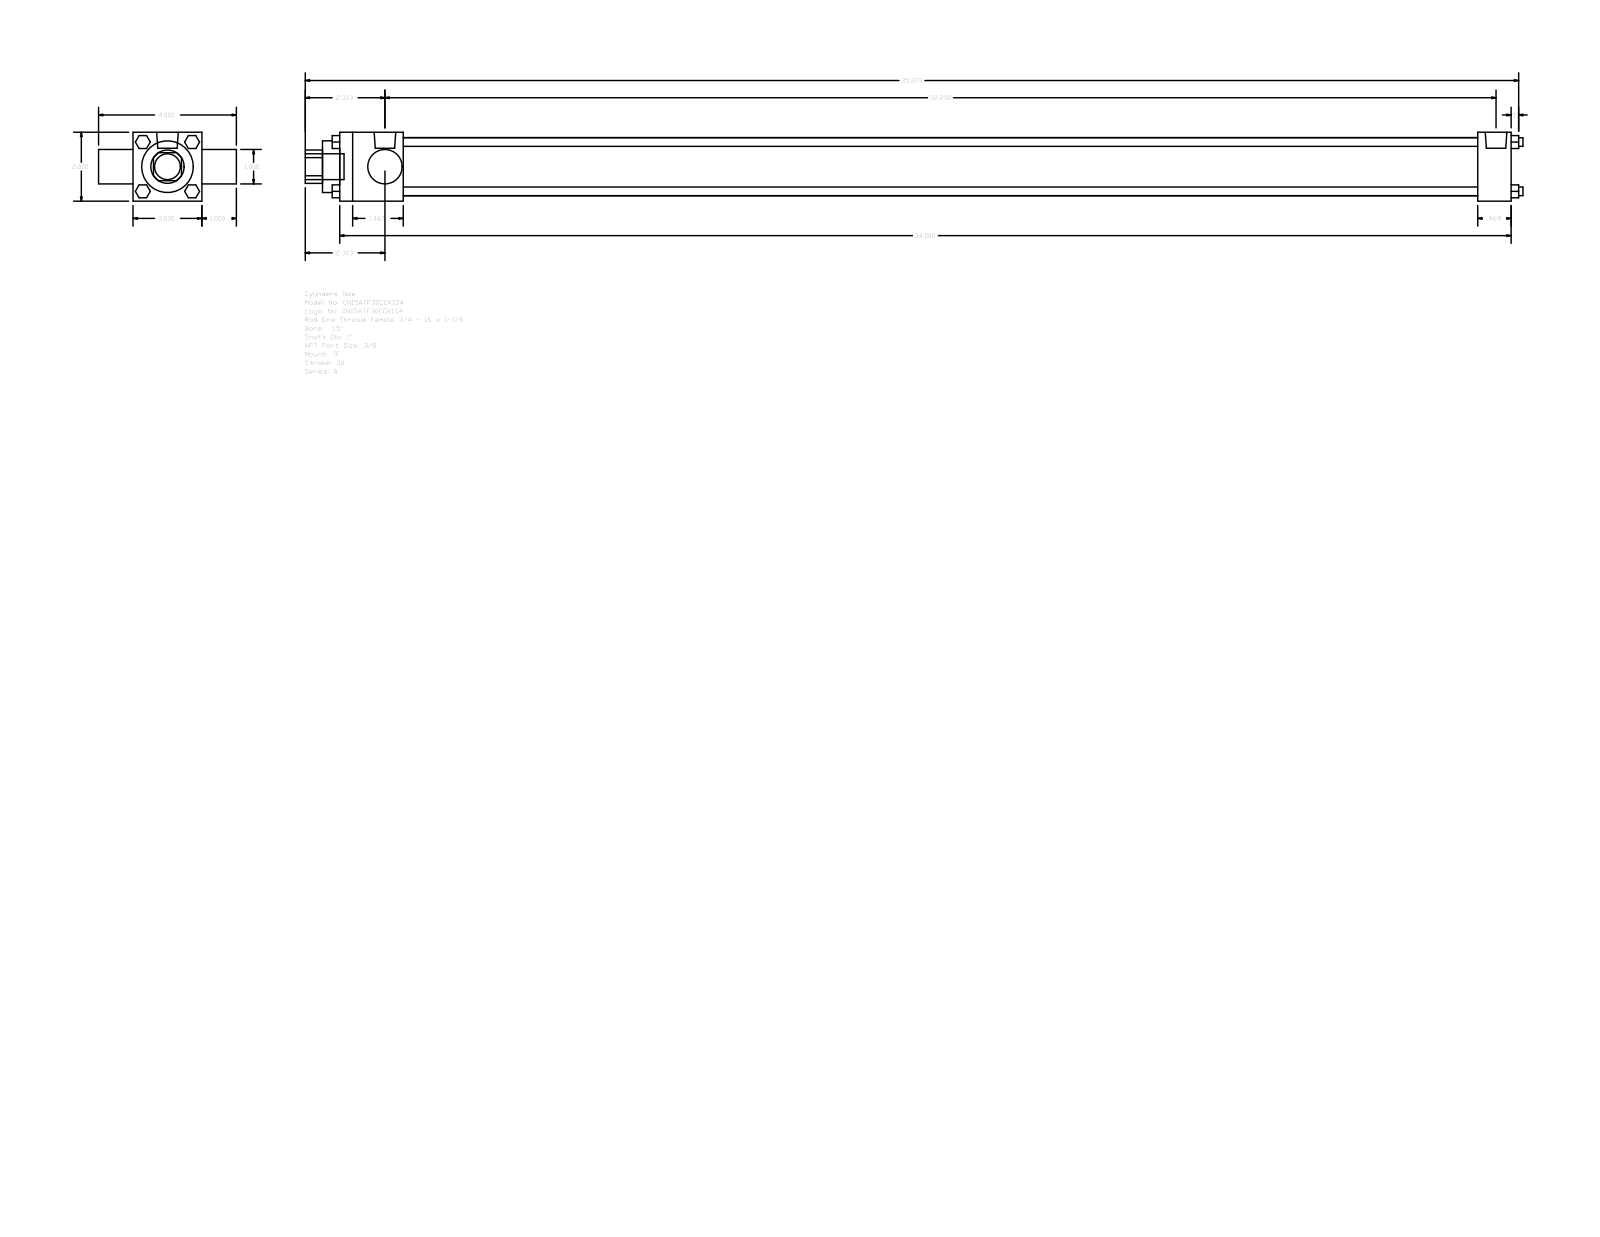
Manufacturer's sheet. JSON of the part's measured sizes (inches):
{"part_name": "A_TF__0150_1", "step_written_by": "GSSL Pune (CONFIG_CONTROL_DESIGN)", "units": "inches", "bodies": {"solids": 0, "faces": 120, "planar": 92, "cylindrical": 28, "other": 0}, "overall_size": [35.344, 4, 2], "round_holes": [[1, 2], [1.5, 1], [1.69, 1]], "round_bosses_or_shafts": [[0.25, 4], [0.219, 3], [0.627, 2], [0.75, 1]], "partial_cylinders_radius": [[0.484, 1]], "face_to_face_distances": [2, 1, 34, 3, 1.844, 33.031, 31.187, 32.156, 0.969, 0.5]}
